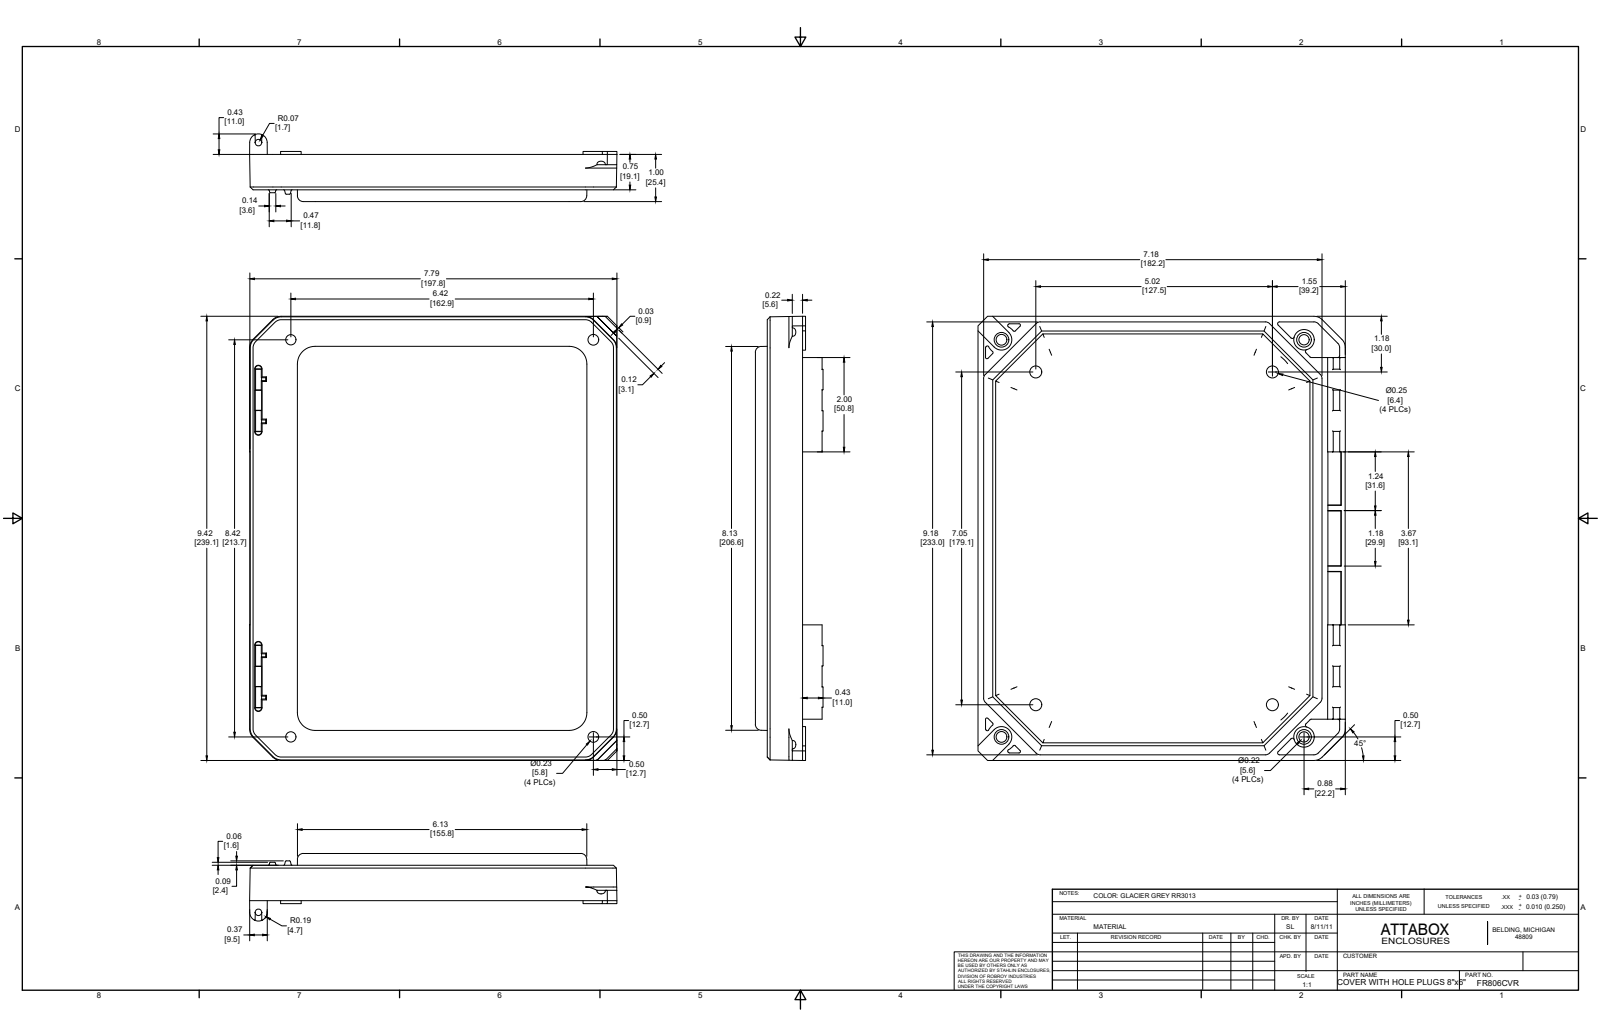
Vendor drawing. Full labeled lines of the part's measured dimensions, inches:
Part name (STEP PRODUCT): FR806CVR
STEP written by: SolidWorks 2019 (AUTOMOTIVE_DESIGN)
Units: inches
Bodies: 1 solid, 577 faces (237 planar, 192 cylindrical, 148 other)
Overall size (bounding box): 9.415 × 7.79 × 1.434
Volume: 19.1 in³ · Surface area: 227 in²
Round holes (diameter × count): ⌀0.253 ×4, ⌀0.219 ×2, ⌀0.227 ×2, ⌀0.313 ×2, ⌀0.137 ×1
Round bosses / shafts (diameter × count): ⌀0.435 ×2
Partial cylindrical surfaces — rounded edges, fillets, slot ends (radius × count): R0.03 ×27, R0.096 ×16, R0.01 ×14, R0.062 ×12, R0.063 ×12, R0.125 ×12, R0.04 ×10, R0.06 ×9
Main face-to-face distances: 0.125, 0.25, 0.125, 0.375, 0.75, 0.625, 0.875, 1, 0.375, 0.625
Hole centre spacings: 0.956, 0.996, 5.018, 5.729, 5.785, 6.415, 7.051, 7.762
